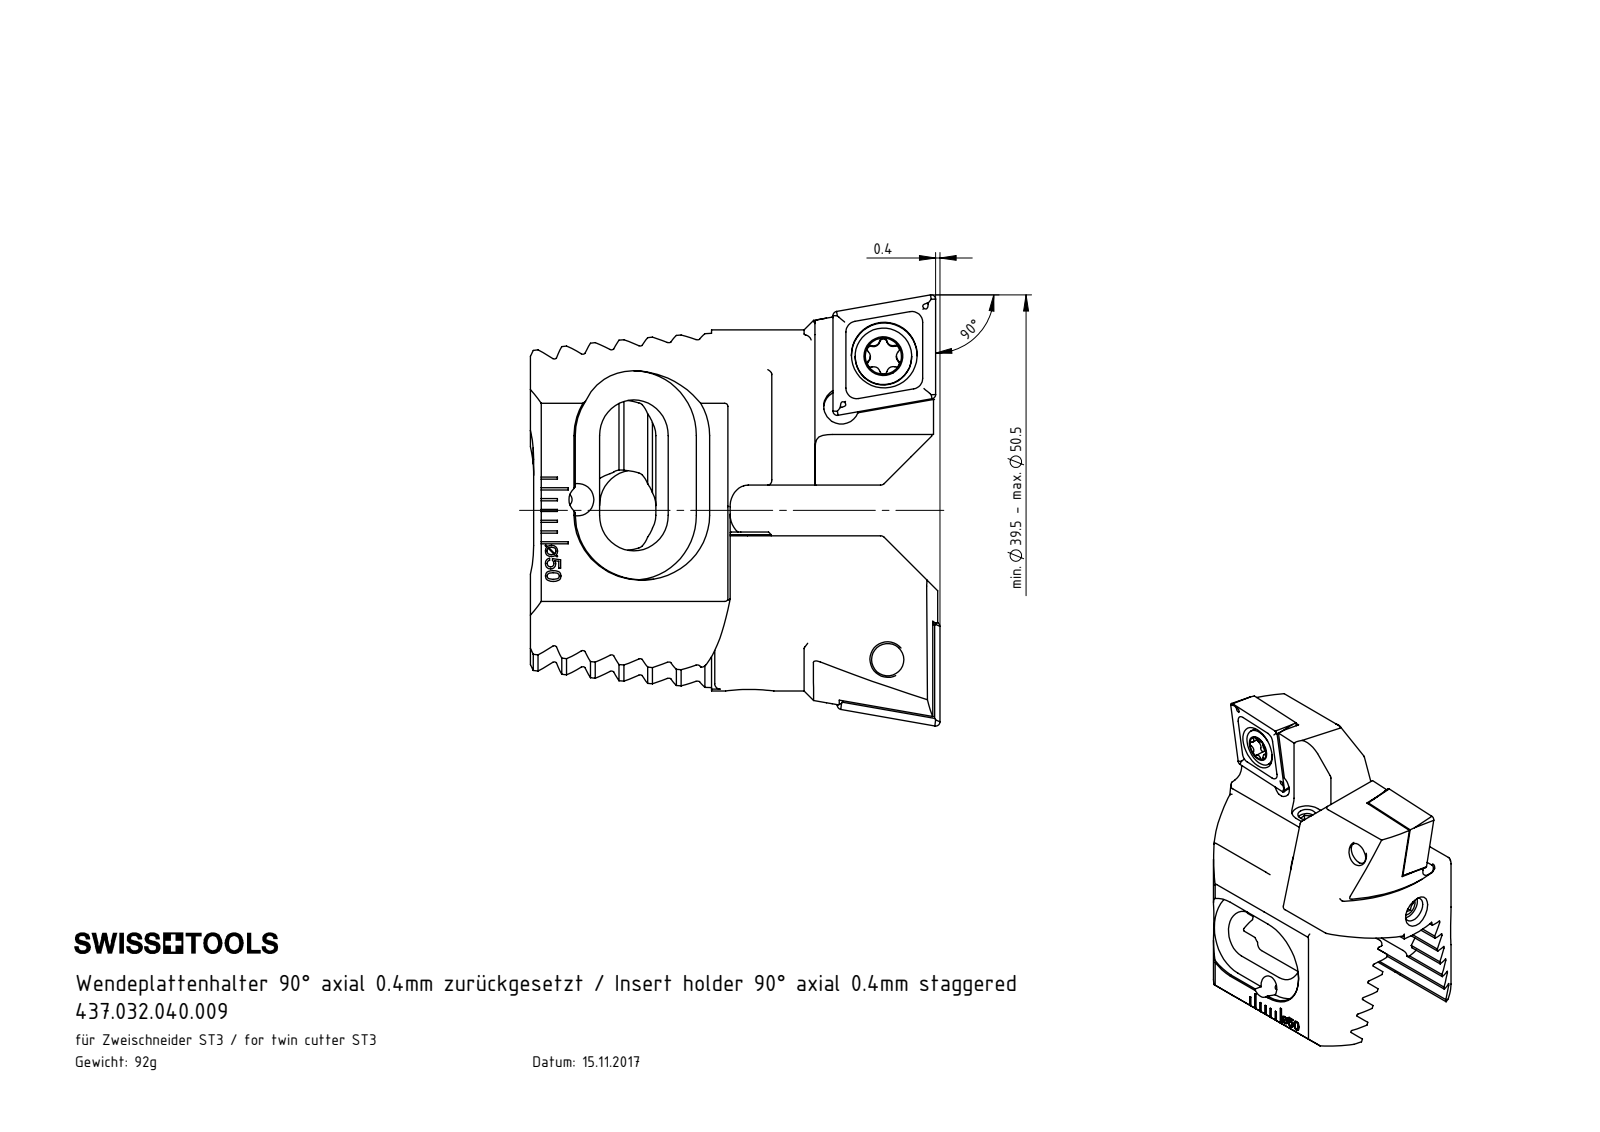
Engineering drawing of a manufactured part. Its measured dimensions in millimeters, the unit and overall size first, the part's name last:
Units: millimetres
Overall size (bounding box): 40 × 38 × 26.2
Round holes (diameter × count): ⌀3.3 ×4, ⌀2 ×2, ⌀4.4 ×2, ⌀6.1 ×2, ⌀1.6 ×1, ⌀2.5 ×1, ⌀3 ×1, ⌀3.5 ×1
Round bosses / shafts (diameter × count): ⌀4 ×4, ⌀5.25 ×2, ⌀3 ×1, ⌀2 ×1
Partial cylindrical surfaces — rounded edges, fillets, slot ends (radius × count): R0.5 ×16, R0.2 ×12, R0.34 ×12, R0.59 ×12, R2 ×4, R3.3 ×4, R6 ×4, R12 ×4
Main face-to-face distances: 2.38, 4.76, 9.53, 7.15, 4.89, 11.91, 7.14, 1.27, 4.77, 0.4
Hole centre spacings: 6.07, 6.19, 28.65, 0.4, 9, 9.11, 19.27, 24.17
Volume: 11 850 mm³ · Surface area: 8 290 mm²
Bodies: 9 solids, 683 faces (326 planar, 143 cylindrical, 214 other)
Part name (STEP PRODUCT): 437.032.040.009; Z32-ER3.001.013_A; ZC3-xxx.001.021_A_versetzt Combi; WCB-ER2.001.009_A (+3 more)
STEP written by: SolidWorks 2017 (CONFIG_CONTROL_DESIGN)
